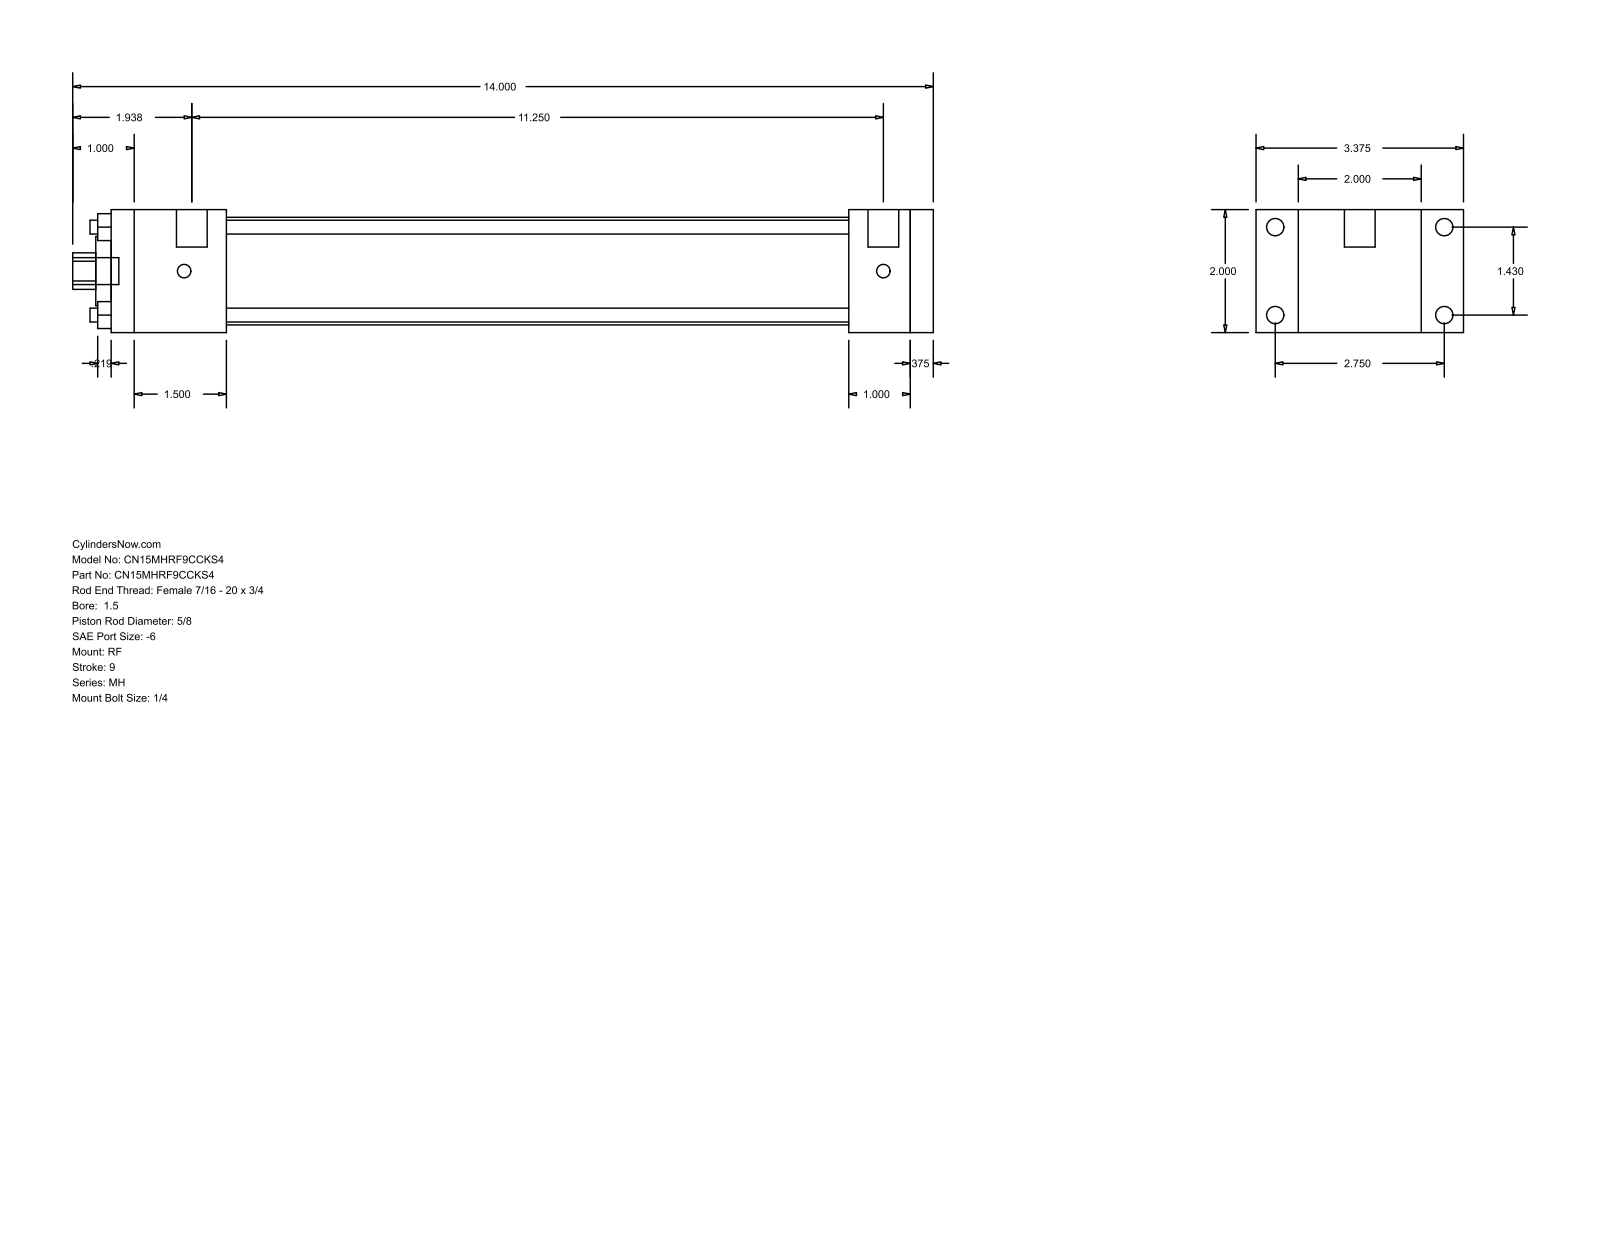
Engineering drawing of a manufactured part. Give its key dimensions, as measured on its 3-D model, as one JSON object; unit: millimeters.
{"part_name": "MH_RF__0150_0.625", "step_written_by": "GSSL Pune (CONFIG_CONTROL_DESIGN)", "units": "millimeters", "bodies": {"solids": 0, "faces": 92, "planar": 64, "cylindrical": 28, "other": 0}, "overall_size": [355.6, 85.72, 50.8], "round_holes": [[5.71, 4], [15.88, 1], [28.57, 1], [44.45, 1]], "round_bosses_or_shafts": [[7.14, 4], [5.56, 4], [12.7, 2], [11.11, 1]], "partial_cylinders_radius": [[7.54, 1]], "face_to_face_distances": [50.8, 9.53, 339.72, 330.19, 17.46, 68.26, 304.8, 25.39, 34.92, 47.62], "hole_center_spacings": [25.68, 36.32, 51.36]}
